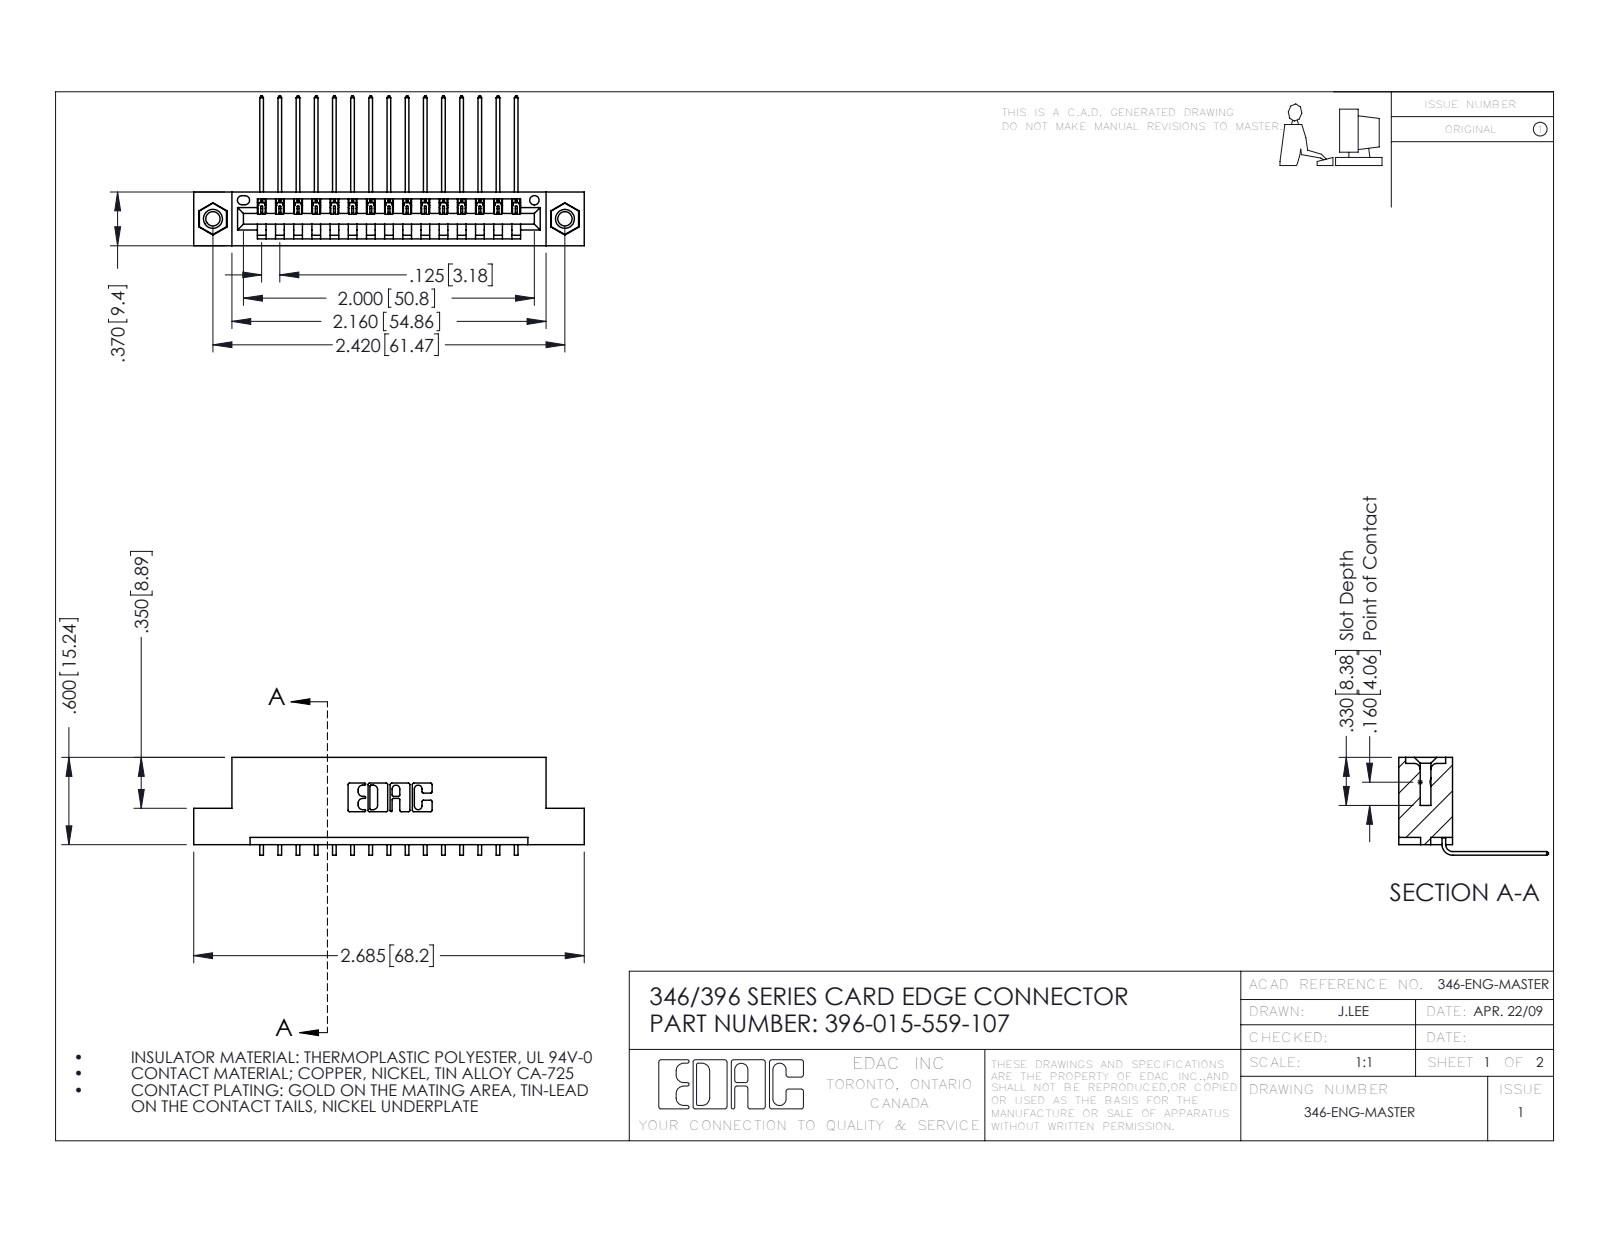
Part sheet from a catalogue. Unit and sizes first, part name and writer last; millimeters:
Units: millimetres
Overall size (bounding box): 68.2 × 26.2 × 17.1
Round holes (diameter × count): ⌀2.5 ×2, ⌀3.2 ×2, ⌀4 ×2, ⌀1.6 ×1
Round bosses / shafts (diameter × count): ⌀3.9 ×2
Partial cylindrical surfaces — rounded edges, fillets, slot ends (radius × count): R0.2 ×30, R0.3 ×22, R0.2 ×6, R0.8 ×6, R0.7 ×3, R0.8 ×2, R1 ×2, R0.4 ×1
Main face-to-face distances: 1.2, 8.2, 6.4, 9.4, 1.8, 0.6, 7.6, 3.8, 5.6, 2.5
Hole centre spacings: 6.2, 56.2, 61.5
Volume: 6 370 mm³ · Surface area: 8 013 mm²
Bodies: 18 solids, 1082 faces (738 planar, 328 cylindrical, 16 other)
Part name (STEP PRODUCT): 396-015-559-107; 345-292-001_558 559 Tail - 1; 345-250-001_345-250-005-103; 346 Part_Flush Mounting Lugs - 0.156 Dia-TI
STEP written by: SolidWorks 2016 (CONFIG_CONTROL_DESIGN)
